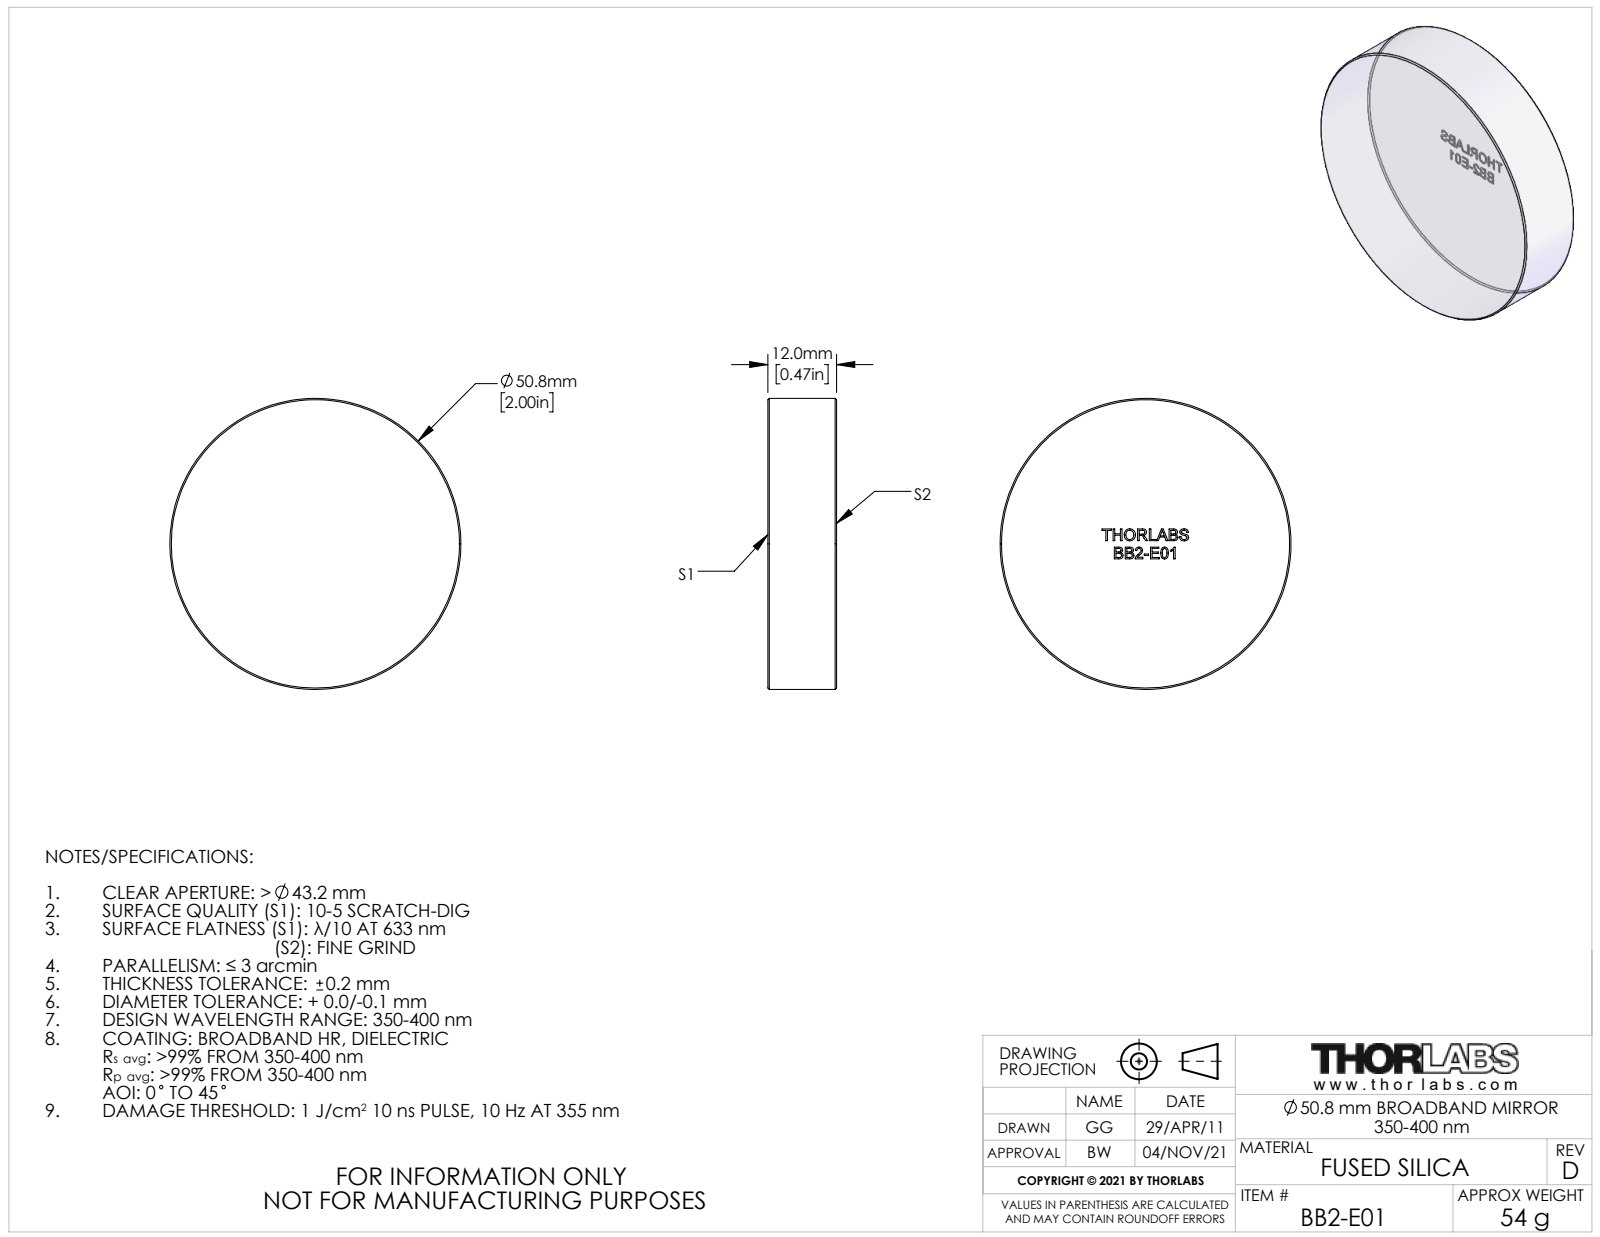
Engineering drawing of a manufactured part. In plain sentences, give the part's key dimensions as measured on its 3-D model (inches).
The part is named "22376-E0W". Its 3-D file was written by "SolidWorks 2016 (CONFIG_CONTROL_DESIGN)". It is 1 solid with 218 faces: 129 planar, 2 cylindrical and 87 other. Overall it measures 2 by 2 by 0.472 inches. Its volume is 1.484 cubic inches and its surface area 9.179 square inches. Round bosses or shafts: 1 of diameter 2. The main face-to-face distances are 0.472, 0.124, 0.081, 0.062, 0.218, 0.159, 0.034, 0.1, 0.205, 0.072.
